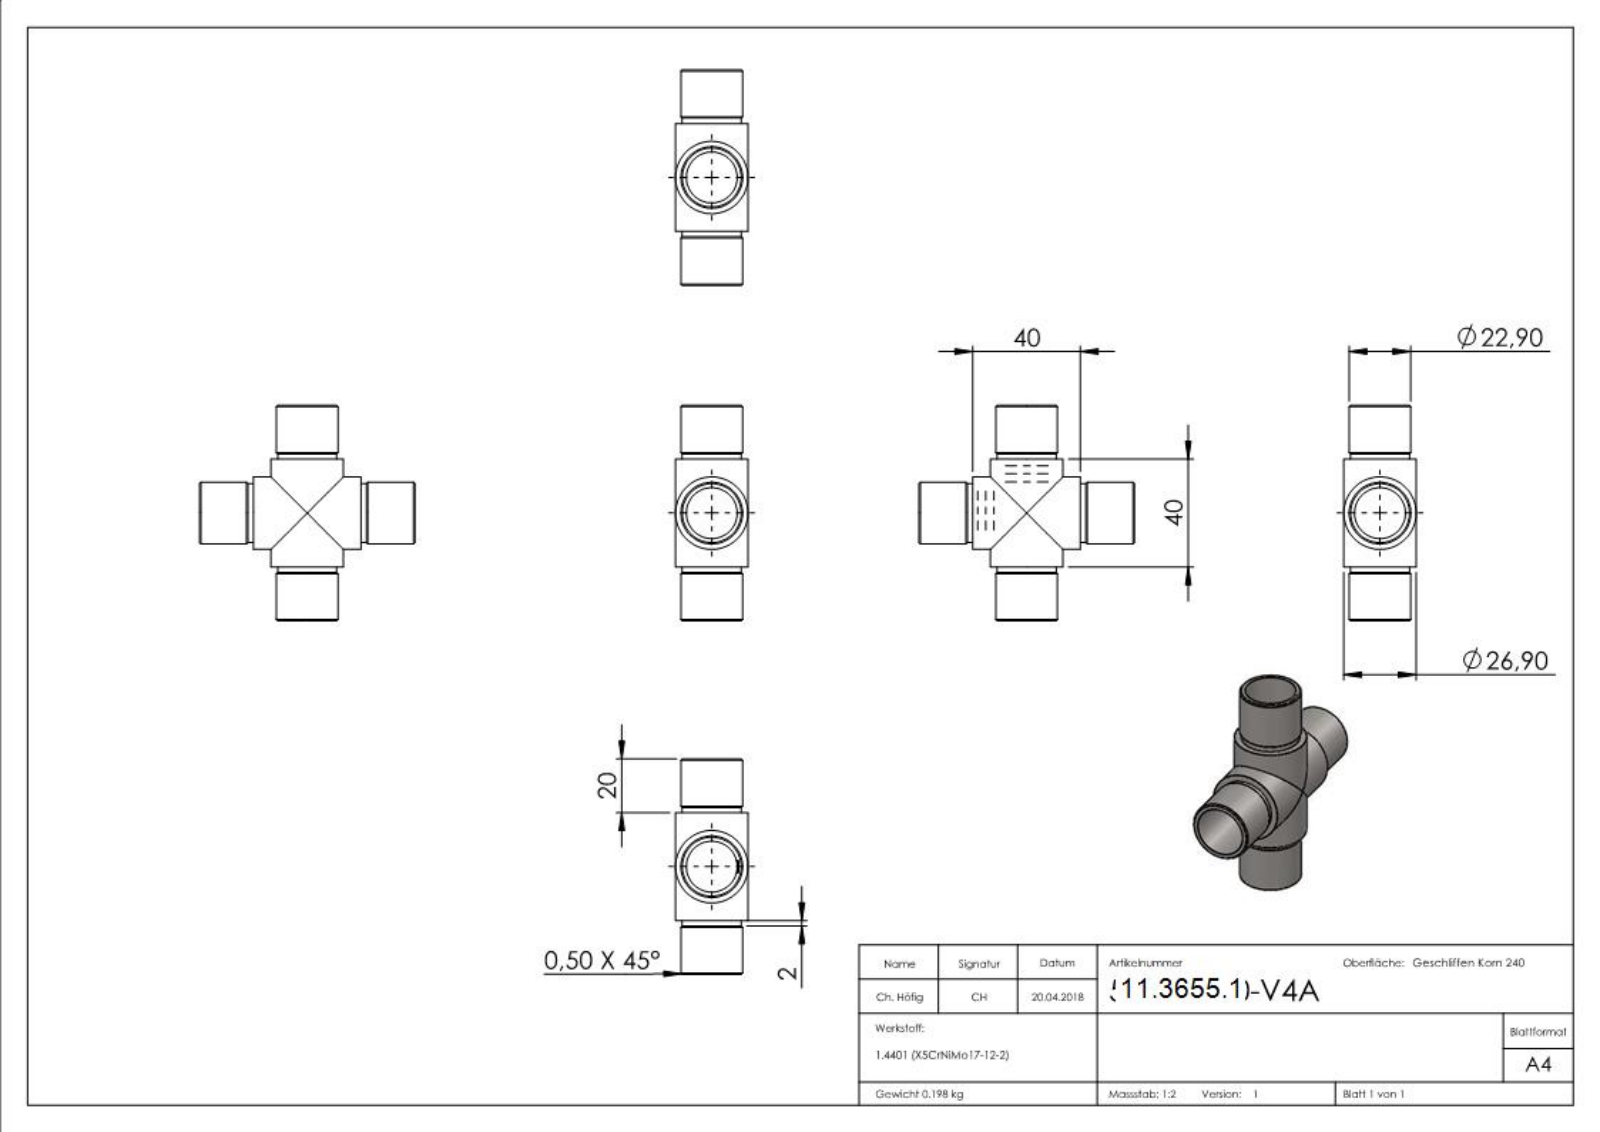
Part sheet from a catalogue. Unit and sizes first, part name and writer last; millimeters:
Units: millimetres
Overall size (bounding box): 80 × 80 × 26.9
Round holes (diameter × count): ⌀19 ×2
Round bosses / shafts (diameter × count): ⌀26.9 ×2, ⌀22.8 ×2, ⌀22.4 ×2
Partial cylindrical surfaces — rounded edges, fillets, slot ends (radius × count): R9.6 ×1
Main face-to-face distances: 20, 60, 40, 80, 17, 63, 3, 43, 46, 0.88
Volume: 24 383 mm³ · Surface area: 18 771 mm²
Bodies: 1 solid, 308 faces (142 planar, 47 cylindrical, 119 other)
Part name (STEP PRODUCT): 56184-320-V4A
STEP written by: SolidWorks 2015 (CONFIG_CONTROL_DESIGN)
